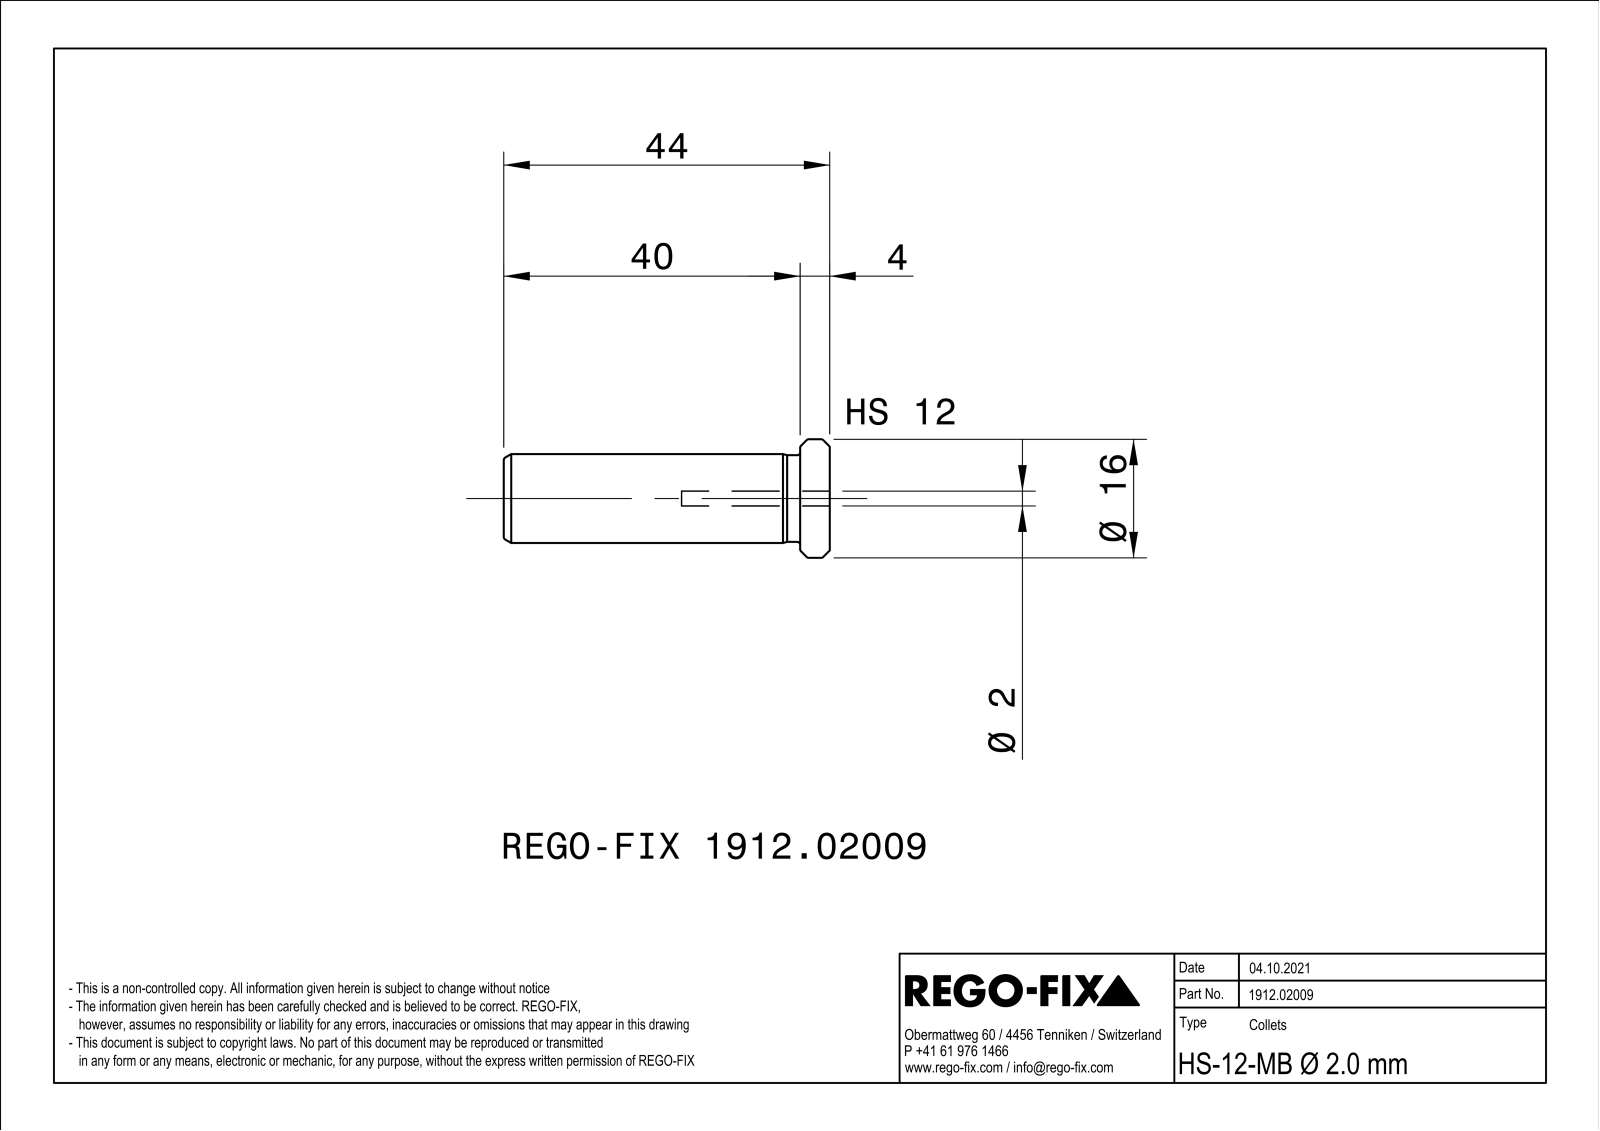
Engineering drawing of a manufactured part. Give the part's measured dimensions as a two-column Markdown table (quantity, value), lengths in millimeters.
| quantity | value |
| --- | --- |
| part name | NOCUT |
| STEP written by | SIEMENS PLM Software Solid Edge ST10 (AUTOMOTIVE_DESIGN) |
| units | millimeters |
| bodies | 1 solid, 67 faces (18 planar, 15 cylindrical, 34 other) |
| overall size | 44 × 16 × 15.98 |
| volume | 3 568 mm³ |
| surface area | 3 607 mm² |
| round holes (diameter × count) | 2 × 4, 7.8 × 1, 8.2 × 1 |
| round bosses / shafts (diameter × count) | 16 × 1, 12 × 1, 11.7 × 1 |
| main face-to-face distances | 1, 44, 20, 24, 4, 16, 40 |
| hole center spacings | 4.58, 2.64, 2.65 |
